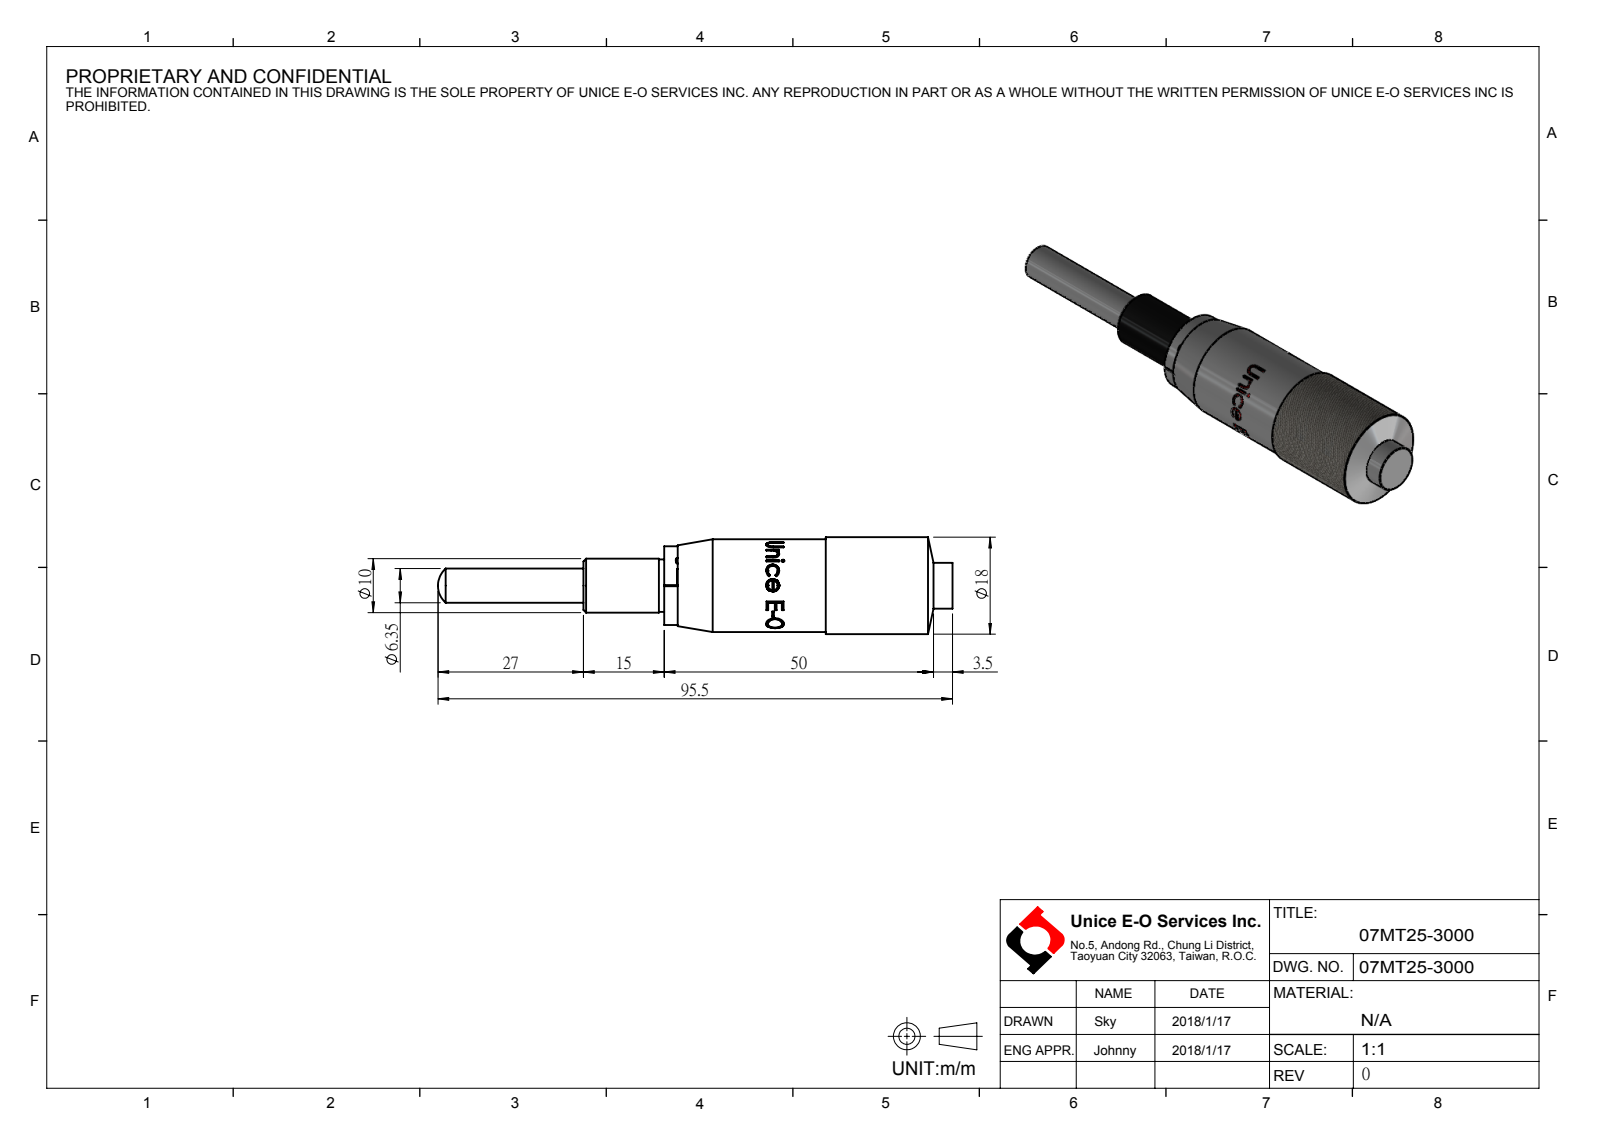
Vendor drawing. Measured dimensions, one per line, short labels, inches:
name: 07MT25-3000
written by: SolidWorks 2016 (AUTOMOTIVE_DESIGN)
unit: in
bodies: 0 solids, 80 faces (20 planar, 27 cylindrical, 33 other)
size: 3.76 × 0.709 × 0.709
bosses: 1× ⌀0.709, 1× ⌀0.677, 1× ⌀0.575, 1× ⌀0.394, 1× ⌀0.384, 1× ⌀0.335, 1× ⌀0.25
rounds: 1× R0.337
face distances: 2.106, 0.591, 2.697, 1.772, 1.181, 0.925, 0.689, 0.098, 1.083, 2.008
